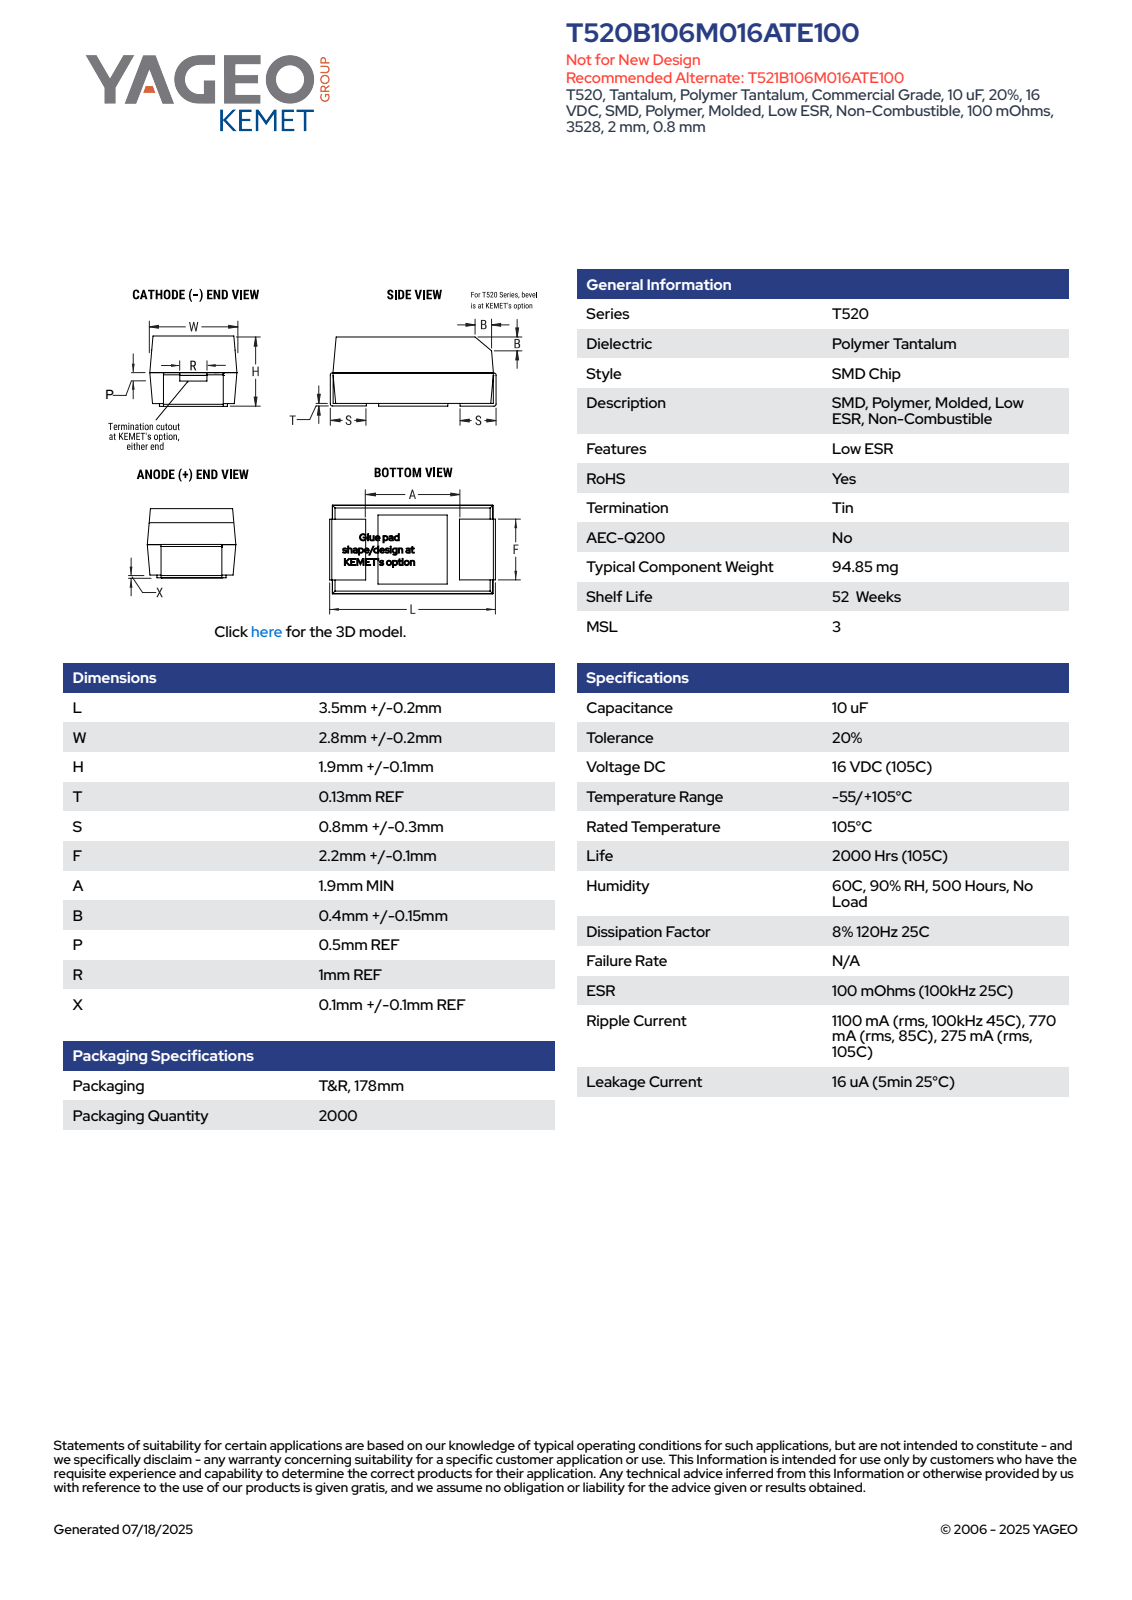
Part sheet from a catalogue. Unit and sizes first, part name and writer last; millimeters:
Units: millimetres
Overall size (bounding box): 3.7 × 3 × 2.1
Main face-to-face distances: 0.9, 1.07, 1.97, 2.98, 3.43, 2.1, 1.03, 3.57, 1, 2.07
Volume: 20 mm³ · Surface area: 80 mm²
Bodies: 7 solids, 100 faces (95 planar, 5 cylindrical, 0 other)
Part name (STEP PRODUCT): Case_Top_1; CTS3528B_L3.7W3H2.1S0.8F2.2R1P0.5B0.4; Case_Bottom_1; Case_Cathode_1 (+1 more)
STEP written by: SolidWorks 2014 (AUTOMOTIVE_DESIGN)
